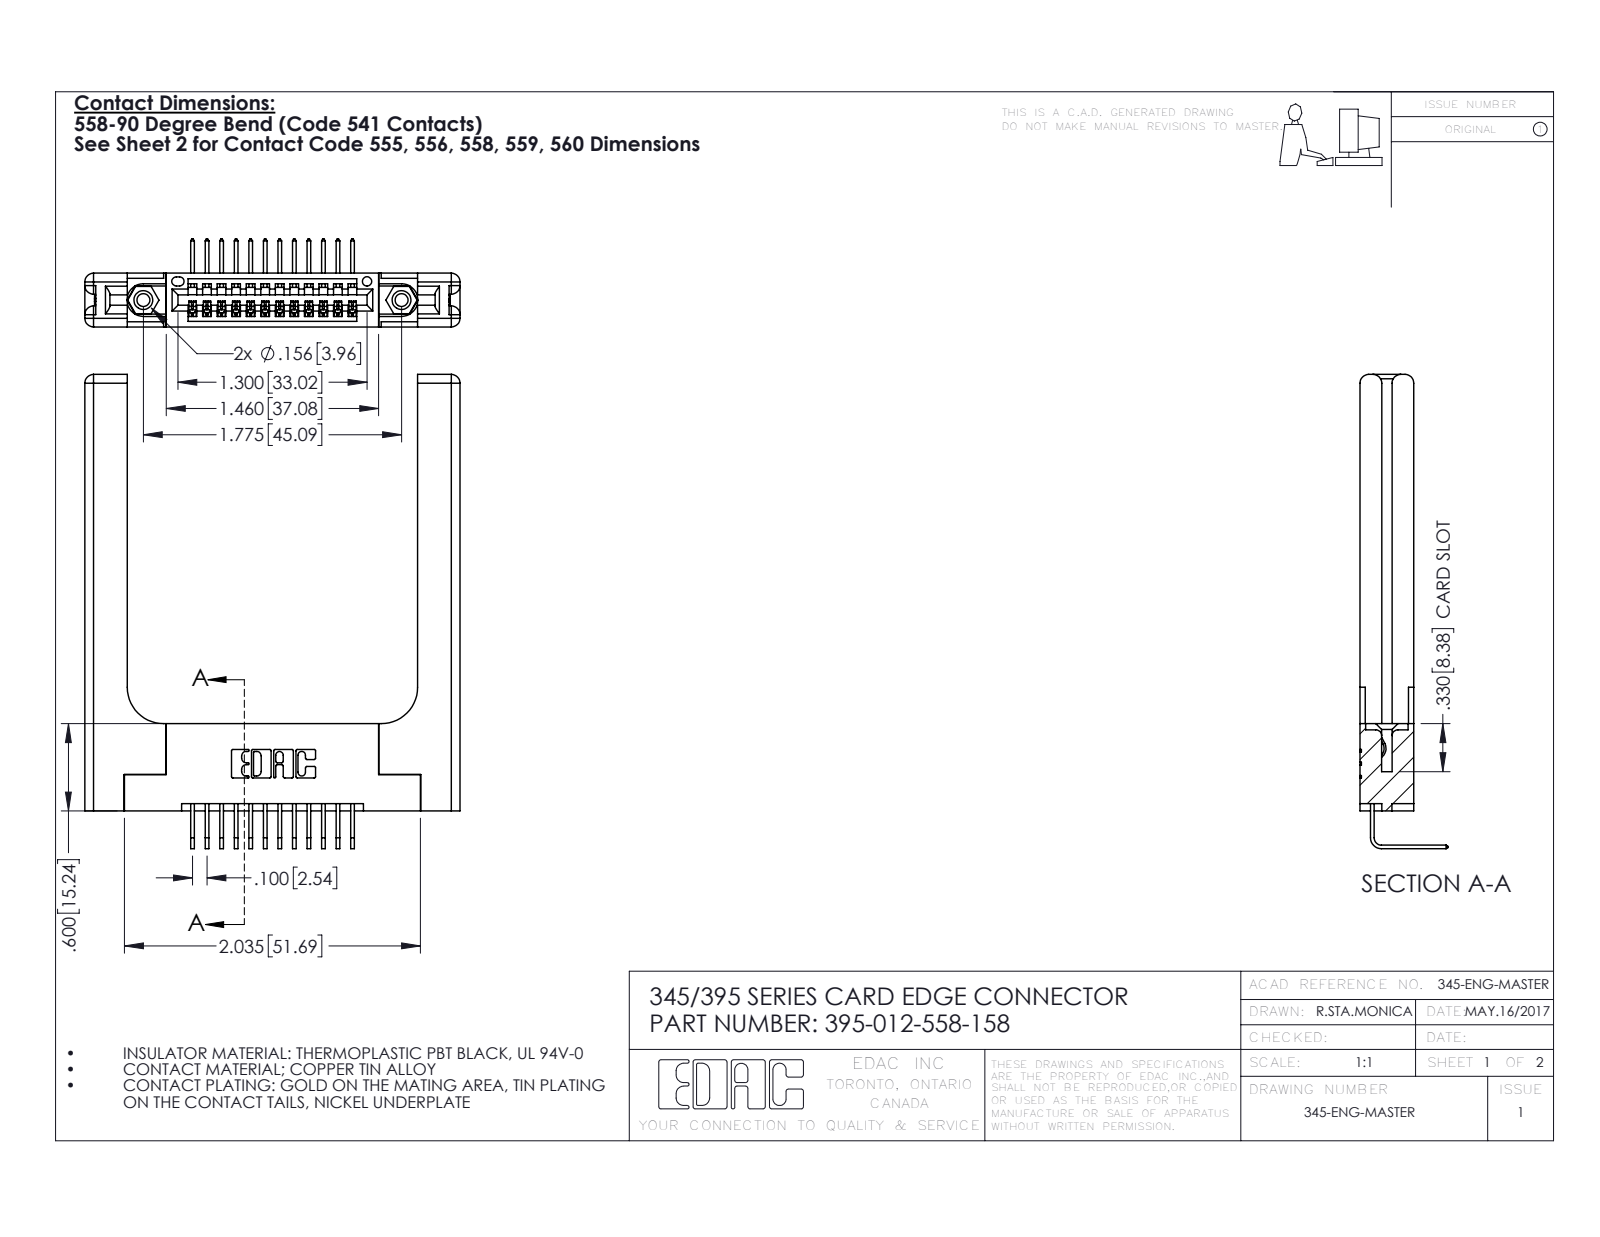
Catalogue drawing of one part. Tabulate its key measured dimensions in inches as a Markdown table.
| quantity | value |
| --- | --- |
| part name | 345-292-001_558 Tail - 2; 345-250-001_345-250-001-102; 345 Part_Flush Mounting Lugs - 0.156 Dia-TH; 345-220-058_345-220-058 (+1 more) |
| STEP written by | SolidWorks 2016 (CONFIG_CONTROL_DESIGN) |
| units | inches |
| bodies | 17 solids, 1102 faces (732 planar, 310 cylindrical, 60 other) |
| overall size | 3.259 × 2.579 × 0.605 |
| volume | 0.886 in³ |
| surface area | 20.35 in² |
| round holes (diameter × count) | 0.089 × 2, 0.125 × 2, 0.156 × 2, 0.064 × 1 |
| round bosses / shafts (diameter × count) | 0.155 × 2 |
| partial cylindrical surfaces (radius × count) | 0.006 × 24, 0.01 × 22, 0.06 × 16, 0.007 × 6, 0.031 × 6, 0.026 × 3, 0.03 × 2, 0.031 × 2 |
| main face-to-face distances | 0.37, 0.072, 0.15, 0.22, 0.077, 0.148, 0.298, 0.2, 1.996, 0.071 |
| hole center spacings | 0.27, 1.543, 1.775 |
